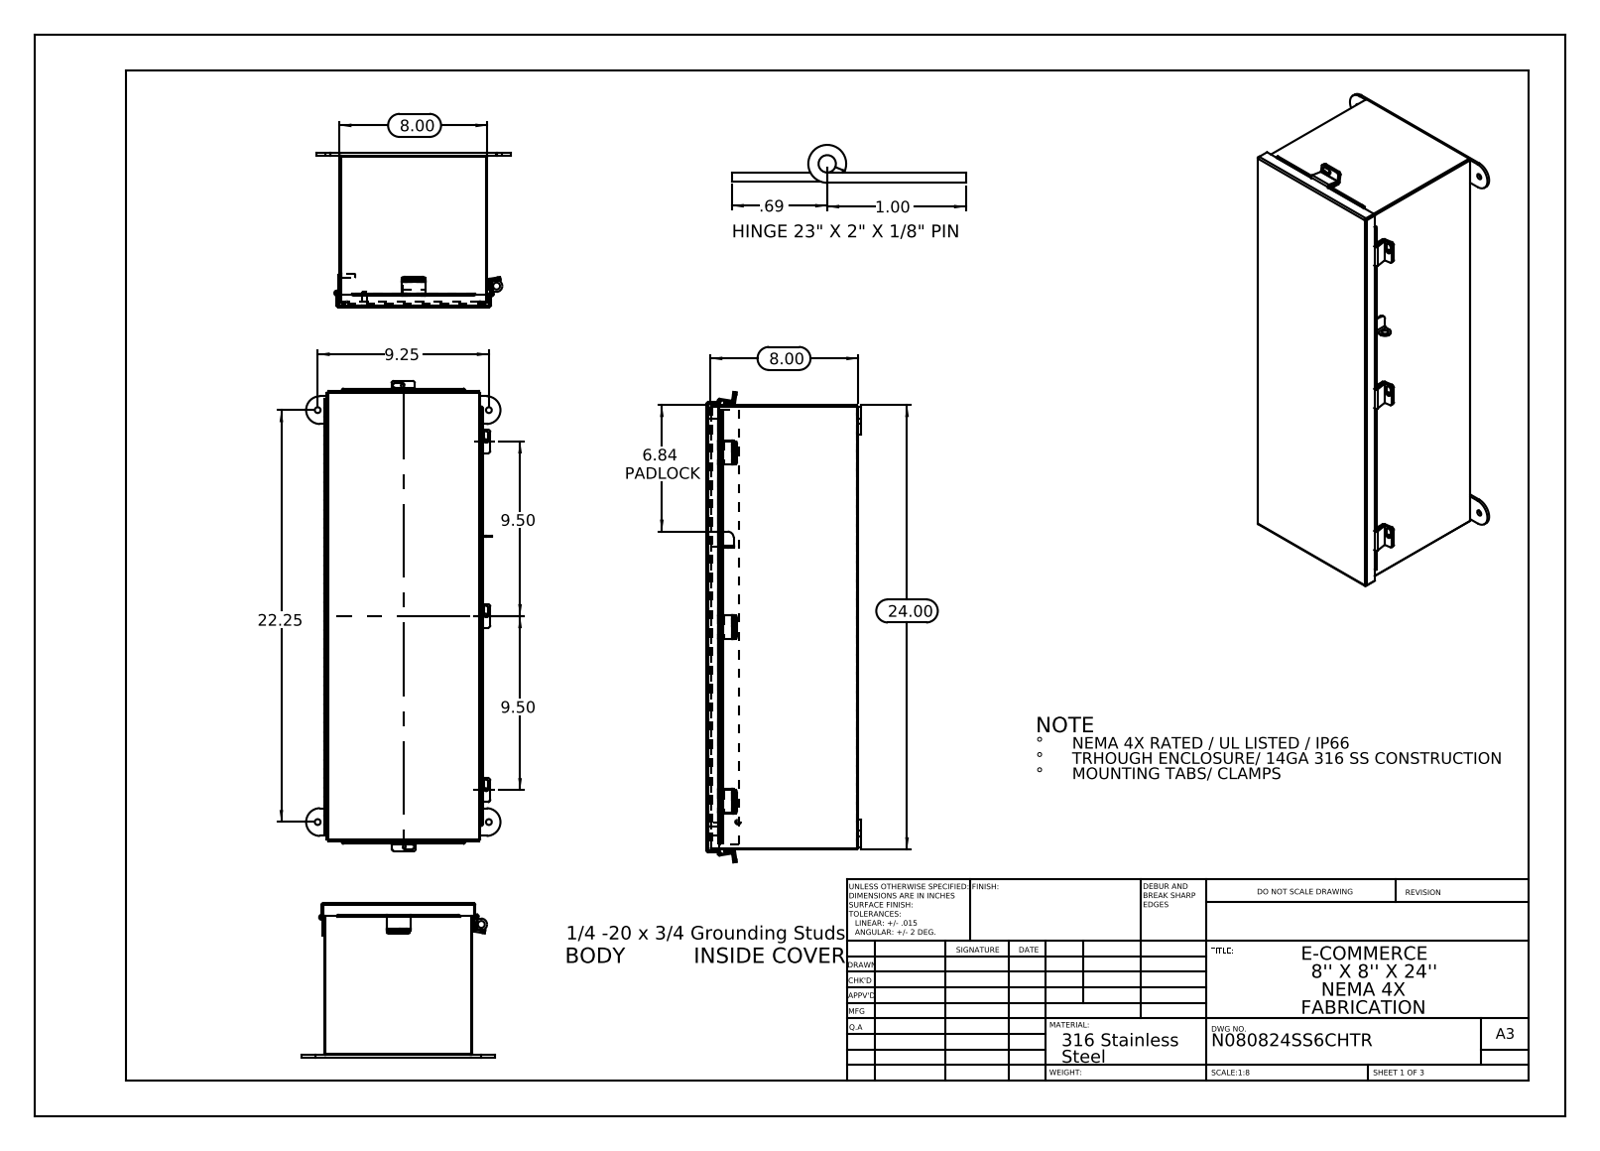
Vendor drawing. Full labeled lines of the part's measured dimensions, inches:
Part name (STEP PRODUCT): N080824SSCHTR JIC Clamp Bracket; N080824SSCHTR JIC Top; HW-CLH-JH-20154; N080824SSCHTR JIC_Cover_Template (+8 more)
STEP written by: SolidWorks 2013 (CONFIG_CONTROL_DESIGN)
Units: inches
Bodies: 21 solids, 898 faces (553 planar, 325 cylindrical, 20 other)
Overall size (bounding box): 25.407 × 10.5 × 8.337
Volume: 80.18 in³ · Surface area: 2 140 in²
Round holes (diameter × count): ⌀0.25 ×5, ⌀0.313 ×4, ⌀0.125 ×1, ⌀0.125 ×1, ⌀0.375 ×1
Round bosses / shafts (diameter × count): ⌀0.315 ×2, ⌀0.236 ×2, ⌀0.273 ×1, ⌀0.25 ×1
Partial cylindrical surfaces — rounded edges, fillets, slot ends (radius × count): R0.125 ×19, R0.009 ×12, R0.013 ×10, R0.088 ×10, R0.133 ×10, R0.083 ×6, R0.1 ×6, R0.75 ×4
Main face-to-face distances: 0.075, 7.925, 8.128, 8, 7.85, 8.203, 8.053, 23.925, 23.85, 24
Hole centre spacings: 9.25, 9.425, 22.25, 24.096, 8.635, 18.85
